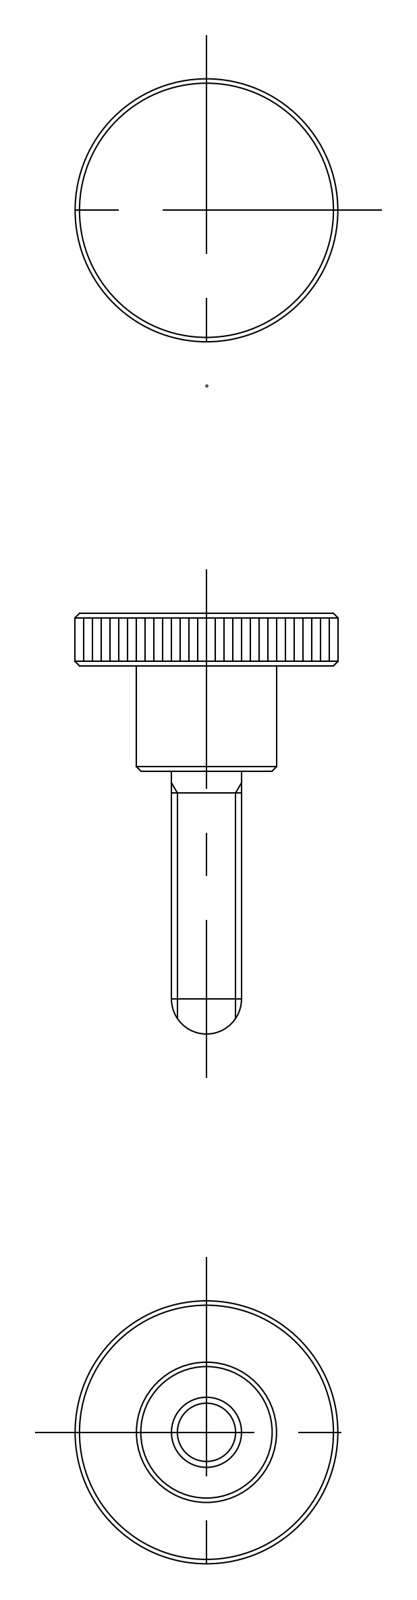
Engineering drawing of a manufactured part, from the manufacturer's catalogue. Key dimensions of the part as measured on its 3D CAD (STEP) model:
Part name (STEP PRODUCT): knob
STEP written by: CADfix (AUTOMOTIVE_DESIGN)
Units: millimetres
Bodies: 1 solid, 16 faces (0 planar, 0 cylindrical, 16 other)
Overall size (bounding box): 48 × 30 × 30
Volume: 8 079 mm³ · Surface area: 3 216 mm²
